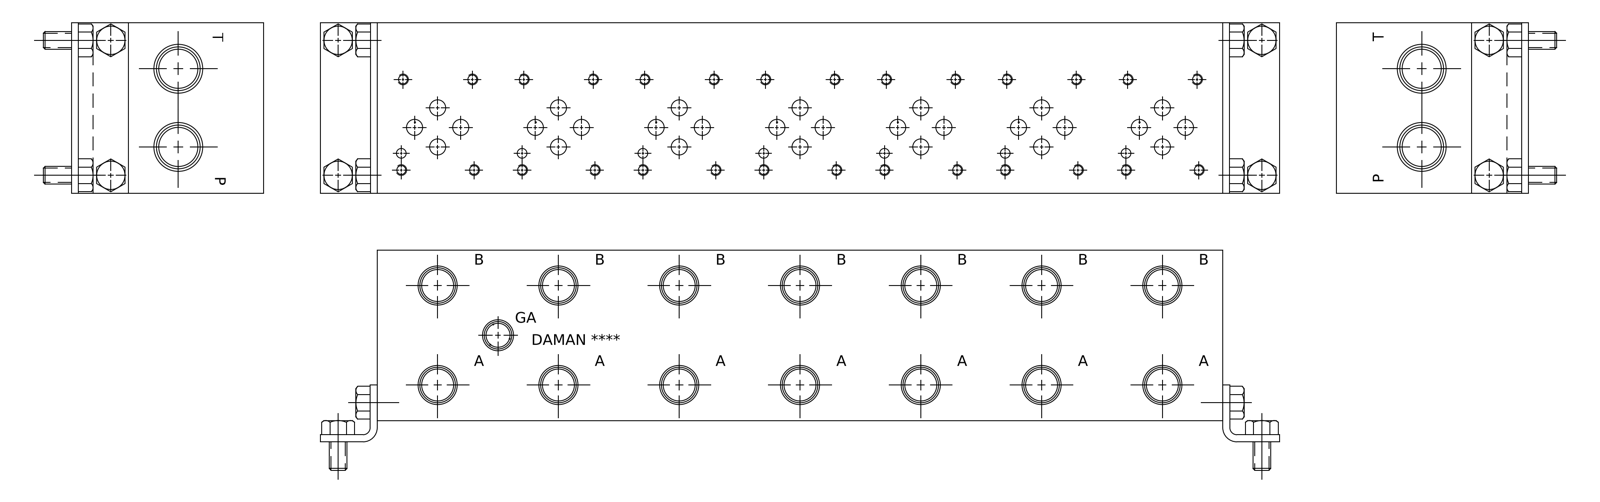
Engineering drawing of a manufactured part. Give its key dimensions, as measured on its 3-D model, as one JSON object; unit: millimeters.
{"part_name": "Part_AD03P072P_3D", "step_written_by": "Autodesk Inventor 2020 (AUTOMOTIVE_DESIGN)", "units": "millimeters", "bodies": {"solids": 1, "faces": 945, "planar": 508, "cylindrical": 137, "other": 300}, "overall_size": [377.82, 76.2, 76.2], "volume_mm3": 2109000, "surface_area_mm2": 153201, "round_holes": [[3.78, 28], [4.83, 28], [7.14, 21], [14.3, 14], [17.3, 14], [3.96, 7], [6.35, 7], [6.53, 2], [7.92, 2], [17.48, 2], [21.59, 2], [10.72, 1]], "face_to_face_distances": [76.2, 377.82, 11.73, 64.47, 11.69, 76.16, 15.37, 362.46, 347.09, 362.45], "hole_center_spacings": [107.95, 53.98, 215.9, 53.97, 161.93, 161.92, 116.74, 118.61]}
